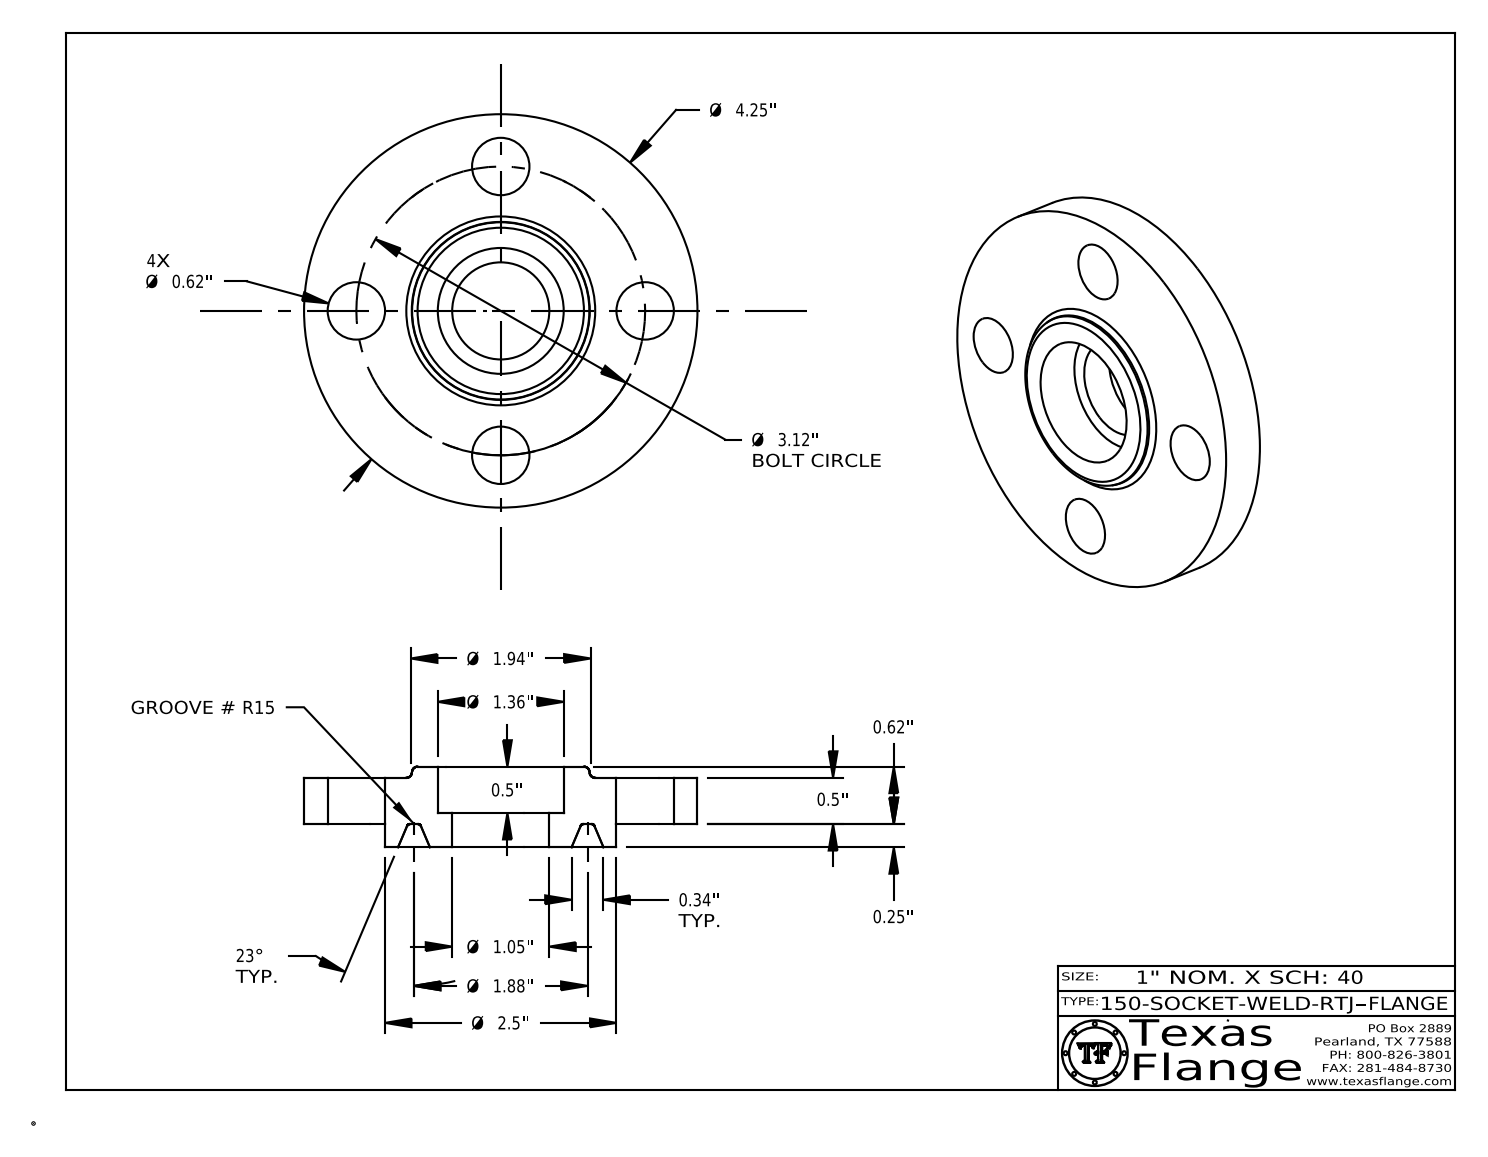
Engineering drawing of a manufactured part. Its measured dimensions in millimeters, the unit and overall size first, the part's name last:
Units: millimetres
Overall size (bounding box): 108 × 108 × 22.1
Round holes (diameter × count): ⌀15.7 ×4, ⌀12.6 ×1, ⌀26.6 ×1, ⌀34.5 ×1
Round bosses / shafts (diameter × count): ⌀0.8 ×8, ⌀108 ×1, ⌀63.5 ×1, ⌀9.9 ×1
Main face-to-face distances: 12.7, 6.4, 19.1, 3, 22.1, 15.7, 9.4, 9.7, 18.7, 12.3
Hole centre spacings: 39.6, 56, 30.3, 73.2, 79.2, 39.6
Volume: 109 300 mm³ · Surface area: 27 430 mm²
Bodies: 1 solid, 422 faces (372 planar, 36 cylindrical, 14 other)
Part name (STEP PRODUCT): 150-SOCKET-WELD-RTJ
STEP written by: CATIA V5 STEP AP214 (AUTOMOTIVE_DESIGN)
